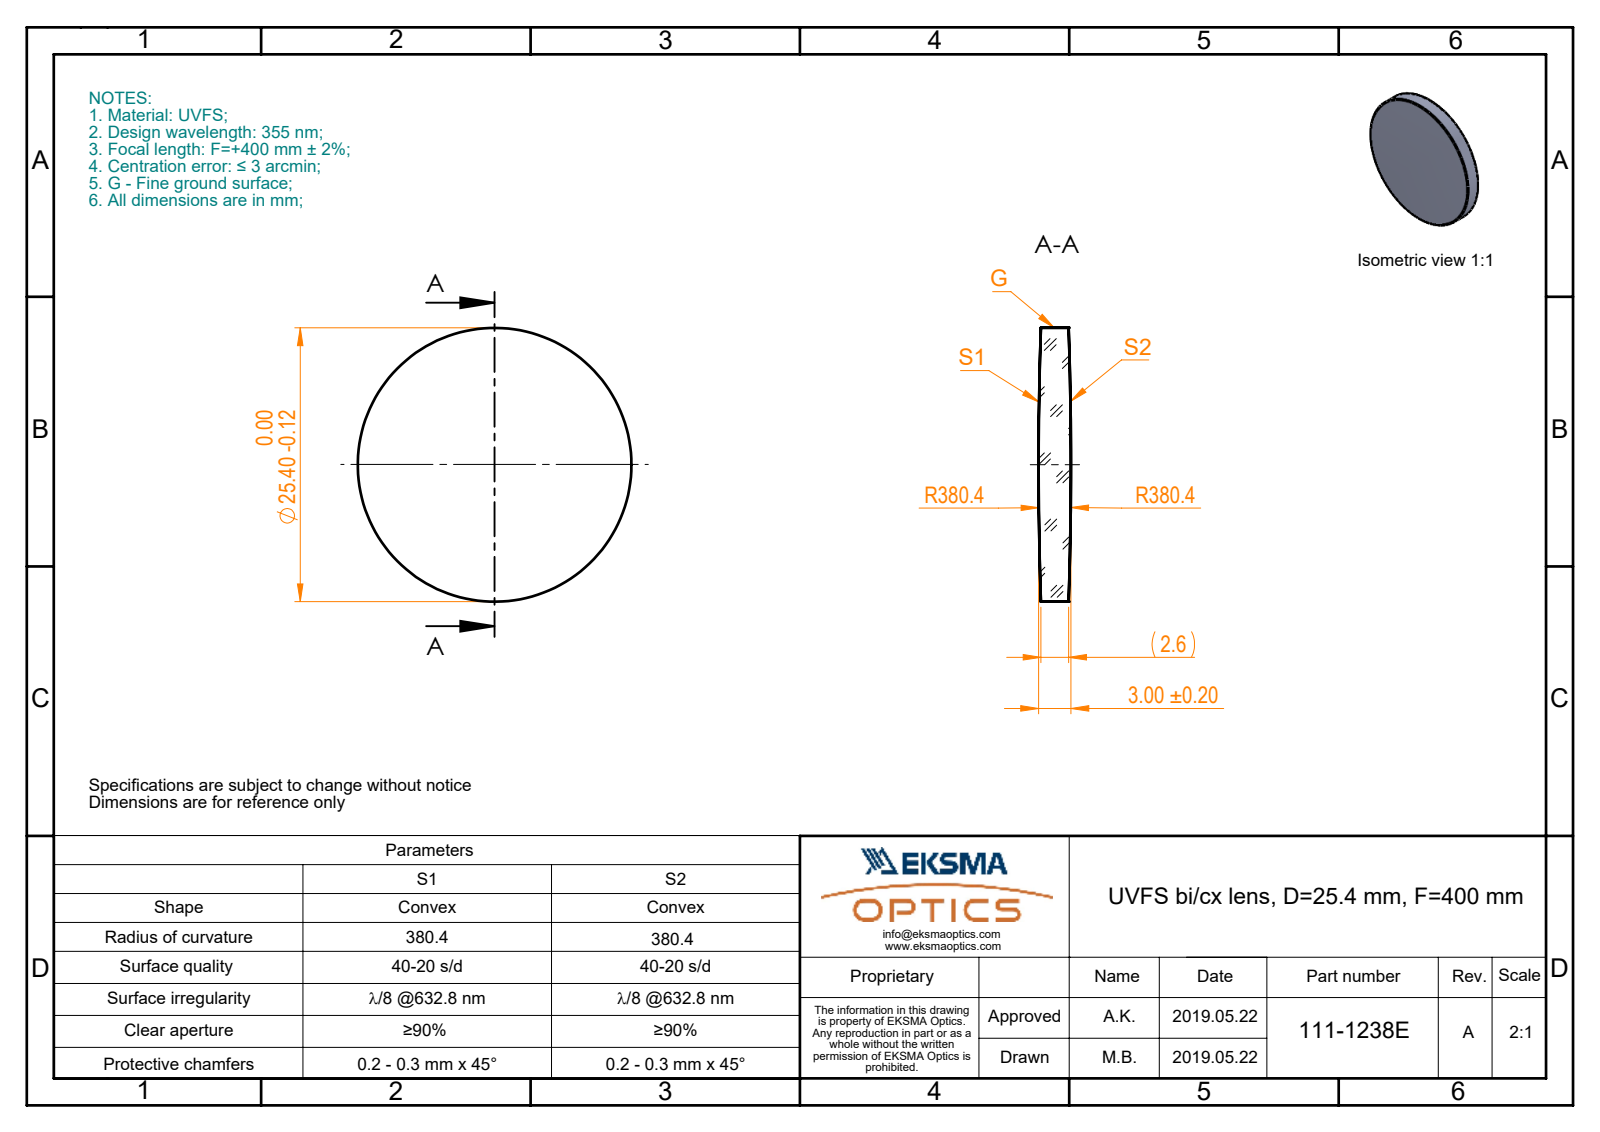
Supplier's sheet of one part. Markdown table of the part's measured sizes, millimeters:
| quantity | value |
| --- | --- |
| part name | 111-1238E UVFS bi-cx 25.4 F400 |
| STEP written by | SolidWorks 2017 (CONFIG_CONTROL_DESIGN) |
| units | millimeters |
| bodies | 1 solid, 6 faces (0 planar, 2 cylindrical, 4 other) |
| overall size | 25.4 × 25.4 × 3 |
| volume | 1 413 mm³ |
| surface area | 1 219 mm² |
| round bosses / shafts (diameter × count) | 25.4 × 1 |
